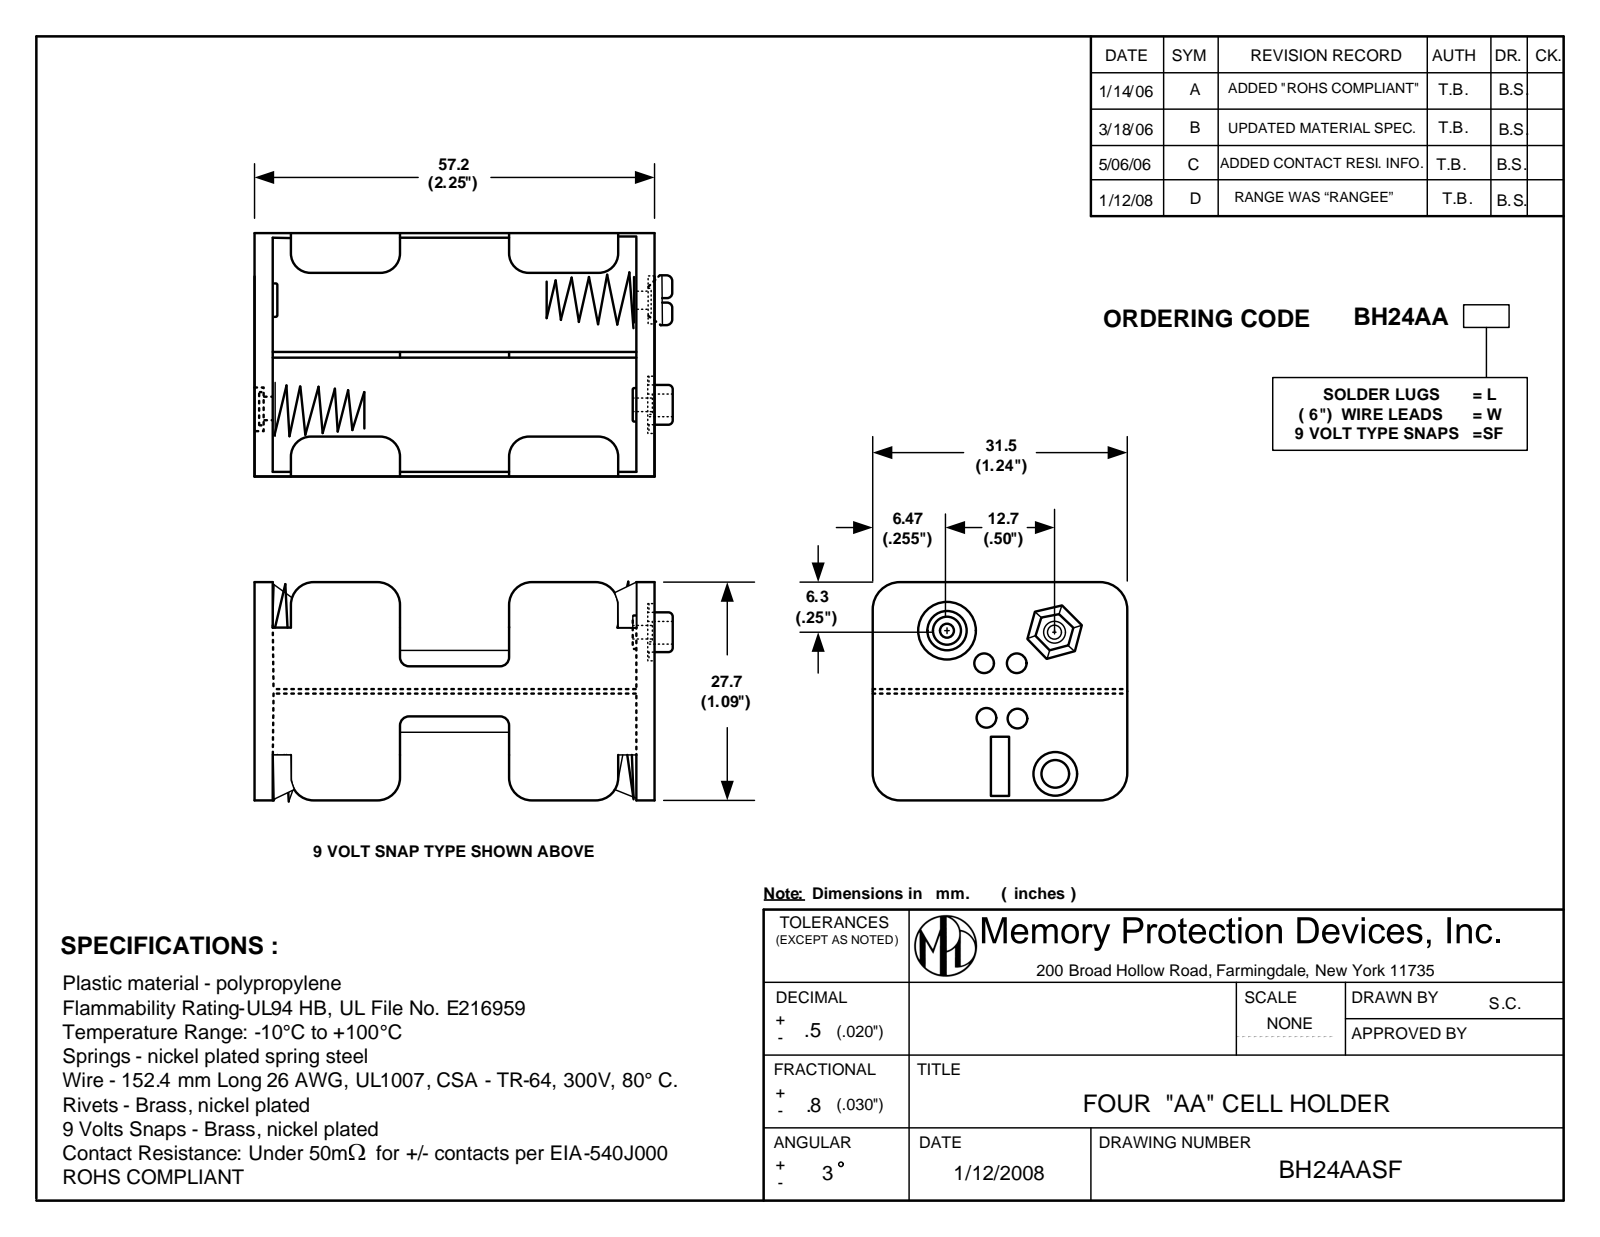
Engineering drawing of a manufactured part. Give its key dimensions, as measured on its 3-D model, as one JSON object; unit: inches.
{"part_name": "BH24AASF", "step_written_by": "SolidWorks 2017 (AUTOMOTIVE_DESIGN)", "units": "inches", "bodies": {"solids": 9, "faces": 734, "planar": 286, "cylindrical": 288, "other": 160}, "overall_size": [2.381, 1.235, 1.08], "volume_in3": 0.624, "surface_area_in2": 22.61, "round_holes": [[0.146, 6], [0.087, 5], [0.091, 4], [0.118, 4], [0.354, 4], [0.06, 3], [0.195, 1]], "round_bosses_or_shafts": [[0.185, 6], [0.244, 4], [0.024, 4], [0.138, 2], [0.312, 1], [0.225, 1]], "partial_cylinders_radius": [[0.008, 22], [0.098, 16], [0.01, 12], [0.015, 12], [0.035, 6], [0.04, 6], [0.118, 4], [0.161, 4]], "face_to_face_distances": [0.043, 0.122, 0.596, 0.596, 1.192, 2.201, 1.235, 2.157, 0.639, 0.639], "hole_center_spacings": [1.496, 0.28, 0.379, 0.458, 0.524, 1.619, 0.13, 0.209]}
